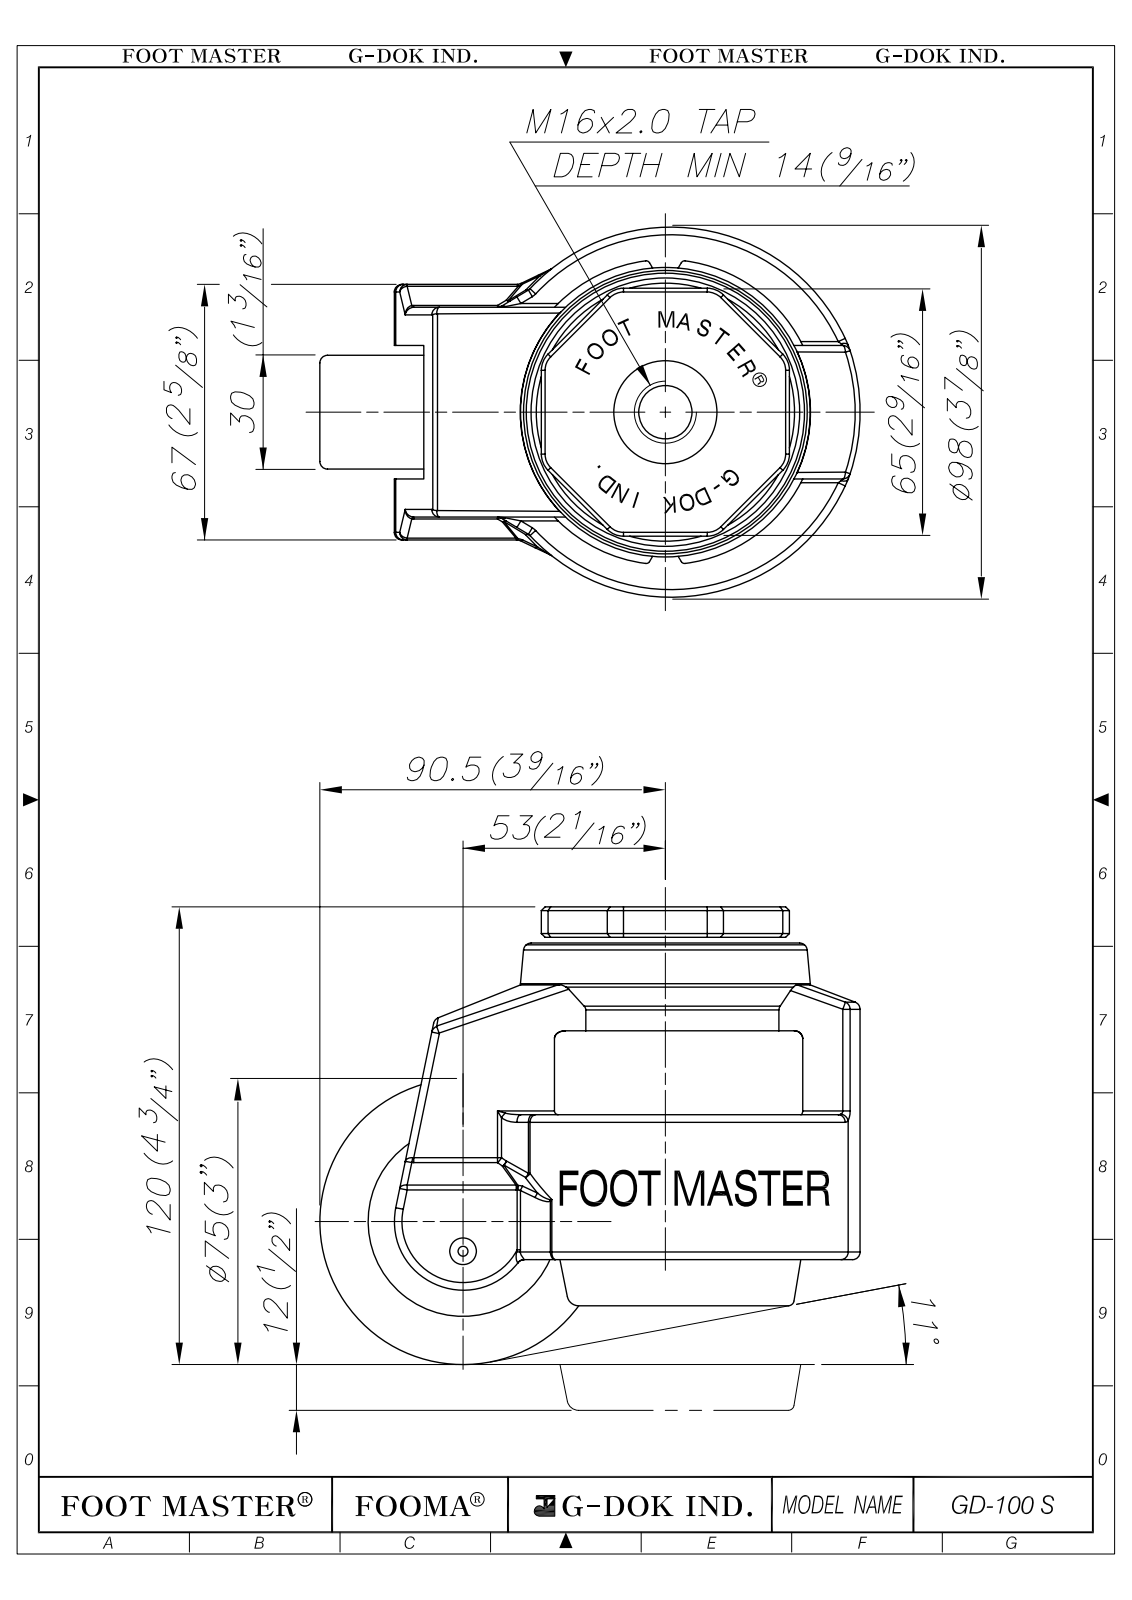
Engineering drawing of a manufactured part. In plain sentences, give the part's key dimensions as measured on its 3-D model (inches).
The part is named "GD-100S". Its 3-D file was written by "Autodesk Inventor 2009 (AUTOMOTIVE_DESIGN)". It is 7 solids with 1590 faces: 468 planar, 306 cylindrical and 816 other. Overall it measures 5.531 by 4.68 by 3.82 inches. Its volume is 35.4 cubic inches and its surface area 204.9 square inches. Round holes: 2 of diameter 0.276, 1 of diameter 0.335, 1 of diameter 0.413, 1 of diameter 0.472, 1 of diameter 1.181, 1 of diameter 1.638, 1 of diameter 1.681, 1 of diameter 1.693, 1 of diameter 1.969, 1 of diameter 3.15. Round bosses or shafts: 3 of diameter 0.118, 1 of diameter 2.874, 1 of diameter 1.677, 1 of diameter 1.102, 1 of diameter 1.063, 1 of diameter 0.787, 1 of diameter 0.78, 1 of diameter 0.63. Partial cylindrical surfaces (rounded edges, fillets, slot ends): 90 of radius 0.039, 65 of radius 0.079, 21 of radius 0.02, 8 of radius 0.197, 5 of radius 0.118, 2 of radius 1.94, 2 of radius 1.979, 1 of radius 0.245. The main face-to-face distances are 0.531, 1.772, 0.039, 0.138, 1.24, 0.394, 0.177, 1.201, 1.378, 1.634. The hole center spacings are 0.079, 0.228, 0.307.
